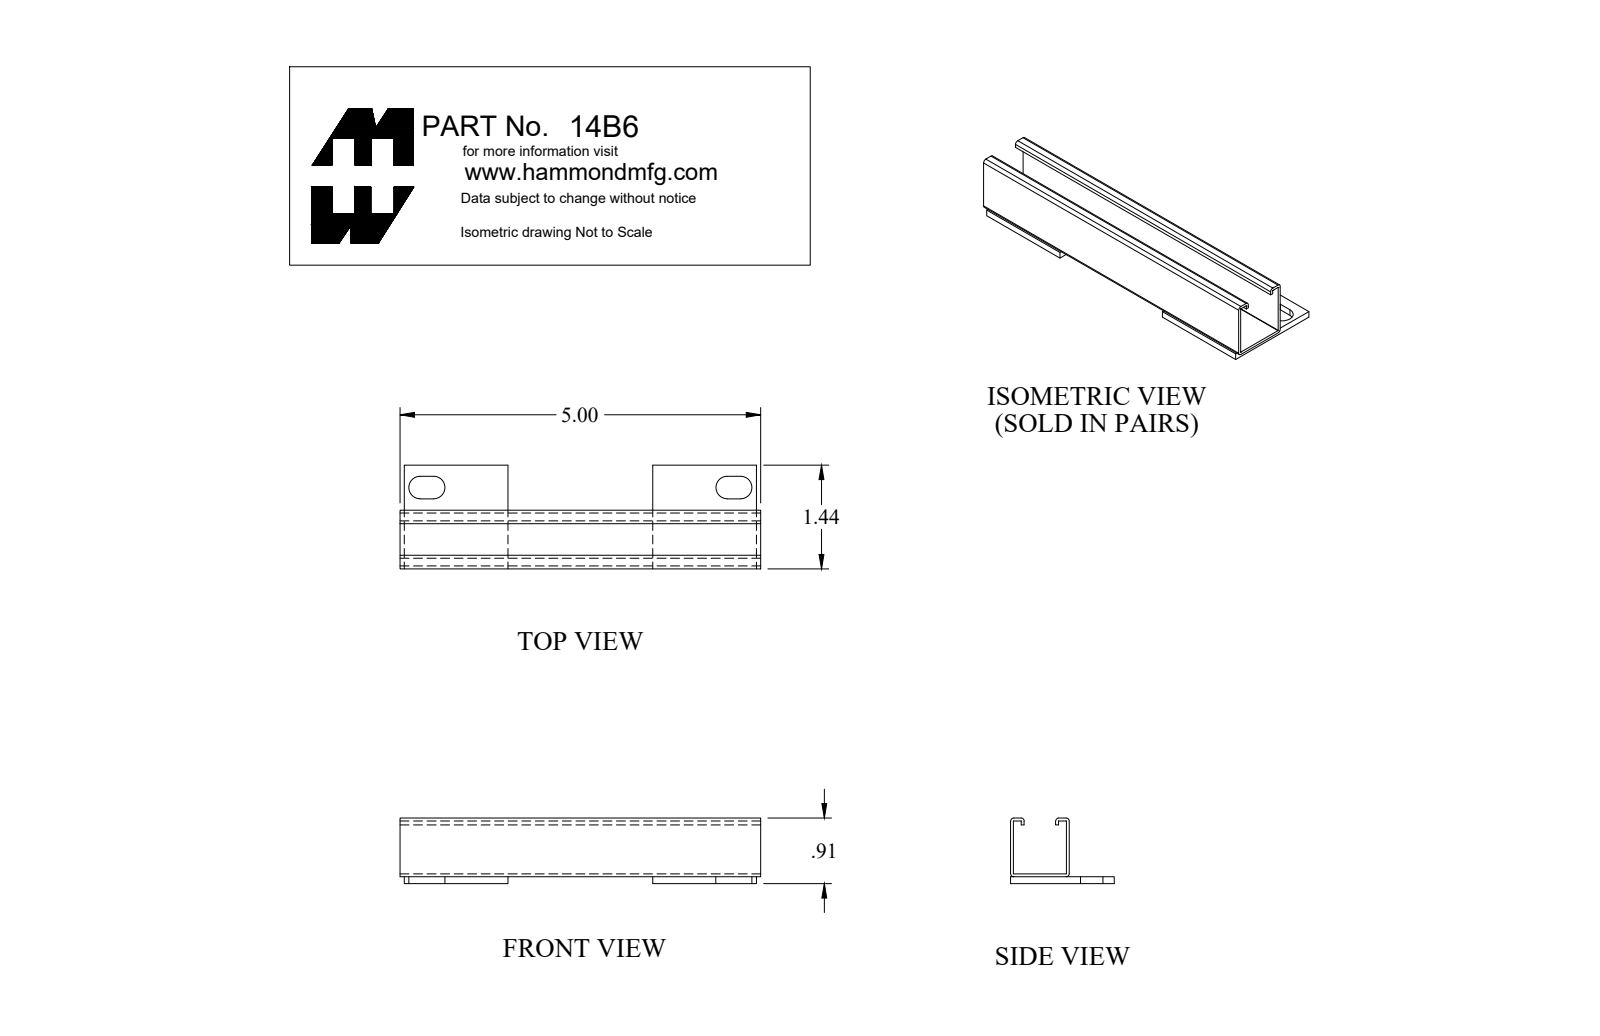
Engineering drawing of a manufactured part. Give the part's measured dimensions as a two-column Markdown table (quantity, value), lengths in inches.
| quantity | value |
| --- | --- |
| part name | 14B6 |
| STEP written by | SolidWorks 2018 (AUTOMOTIVE_DESIGN) |
| units | inches |
| bodies | 3 solids, 50 faces (34 planar, 16 cylindrical, 0 other) |
| overall size | 5 × 1.437 × 0.908 |
| volume | 0.907 in³ |
| surface area | 36.72 in² |
| partial cylindrical surfaces (radius × count) | 0.043 × 6, 0.156 × 4 |
| main face-to-face distances | 0.04, 0.773, 0.095, 0.135, 0.813, 0.733, 0.773, 0.868, 0.908, 0.813 |
